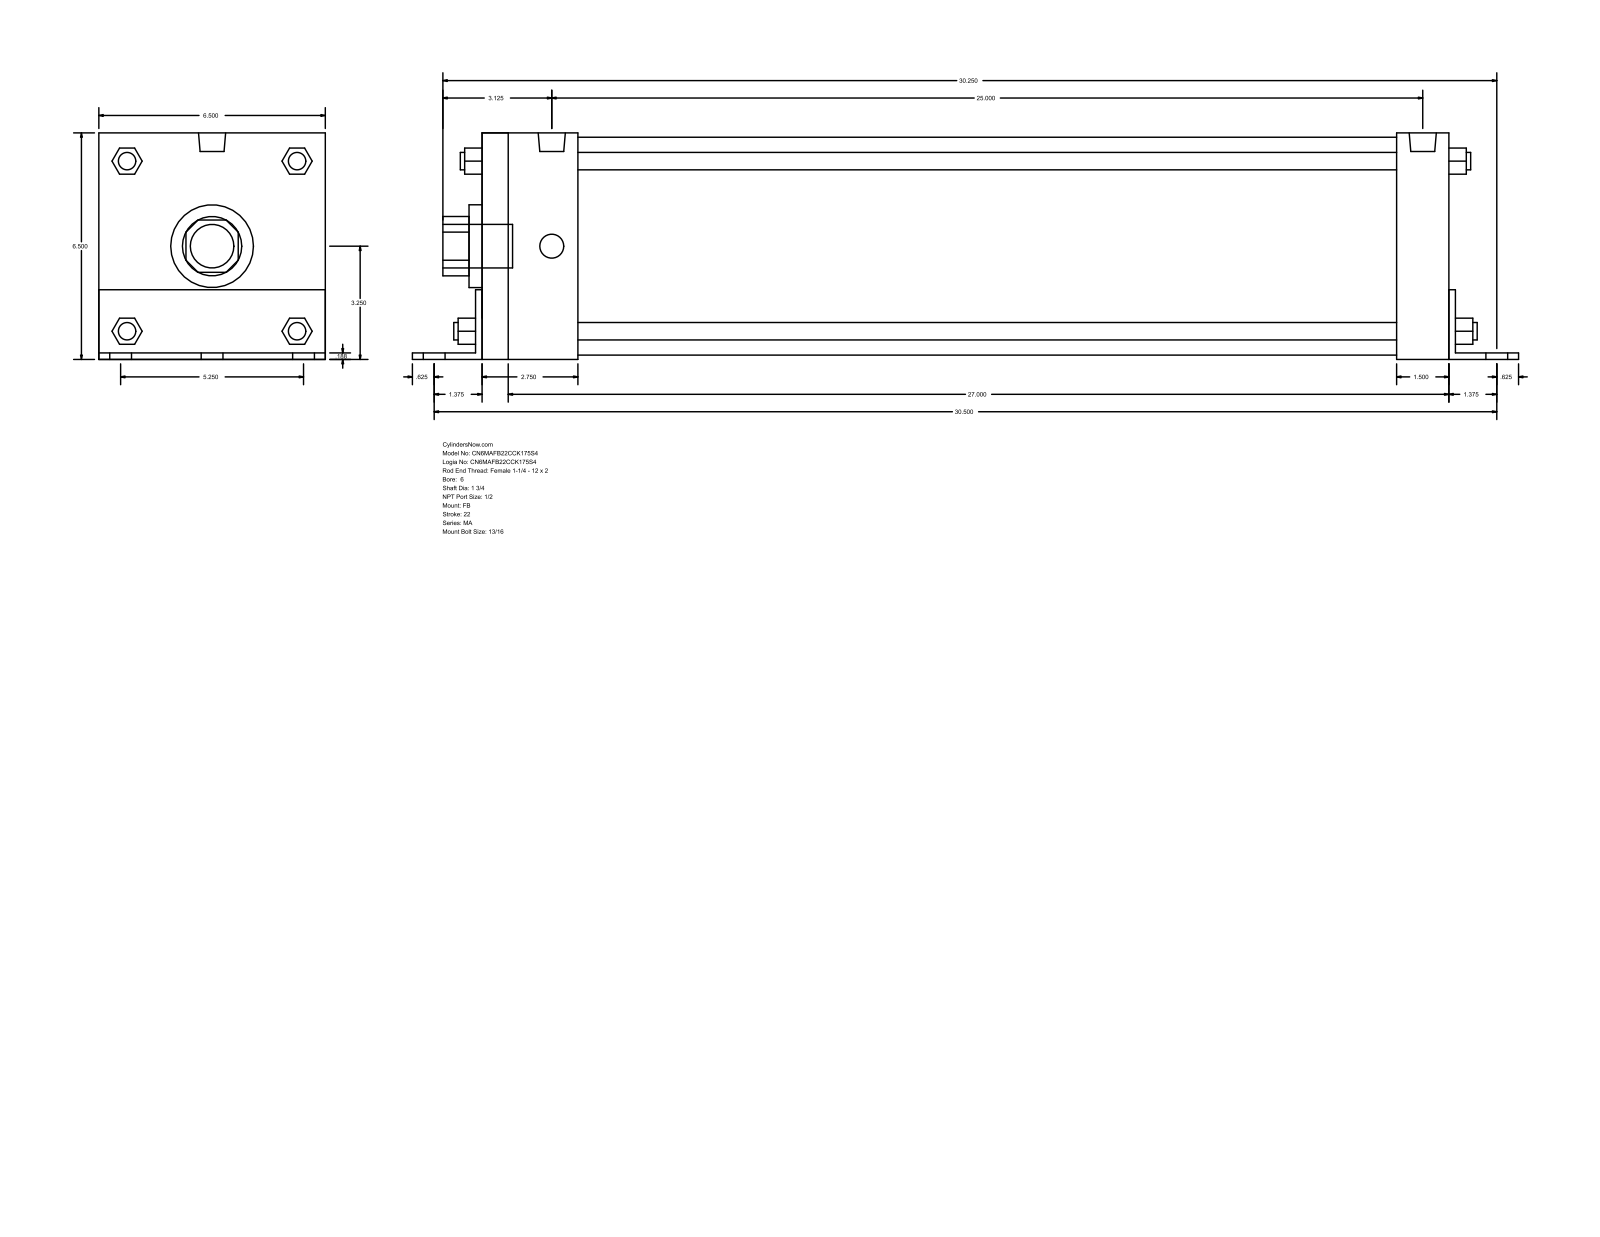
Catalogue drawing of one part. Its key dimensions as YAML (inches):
part_name: "MA_FB__0600_1.75"
step_written_by: "GSSL Pune (CONFIG_CONTROL_DESIGN)"
units: inches
bodies: {solids: 0, faces: 140, planar: 105, cylindrical: 35, other: 0}
overall_size: [31.75, 6.502, 6.5]
round_holes:
  - {diameter: 1.75, count: 1}
  - {diameter: 2.375, count: 1}
  - {diameter: 6.25, count: 1}
round_bosses_or_shafts:
  - {diameter: 0.813, count: 6}
  - {diameter: 0.687, count: 4}
  - {diameter: 0.5, count: 4}
  - {diameter: 0.778, count: 2}
  - {diameter: 1.25, count: 1}
partial_cylinders:
  - {radius: 0.852, count: 1}
  - {radius: 1.262, count: 1}
face_to_face_distances: [6.5, 0.187, 27.75, 6.502, 0.185, 6.315, 0.188, 1.687, 27.938, 27.937]
